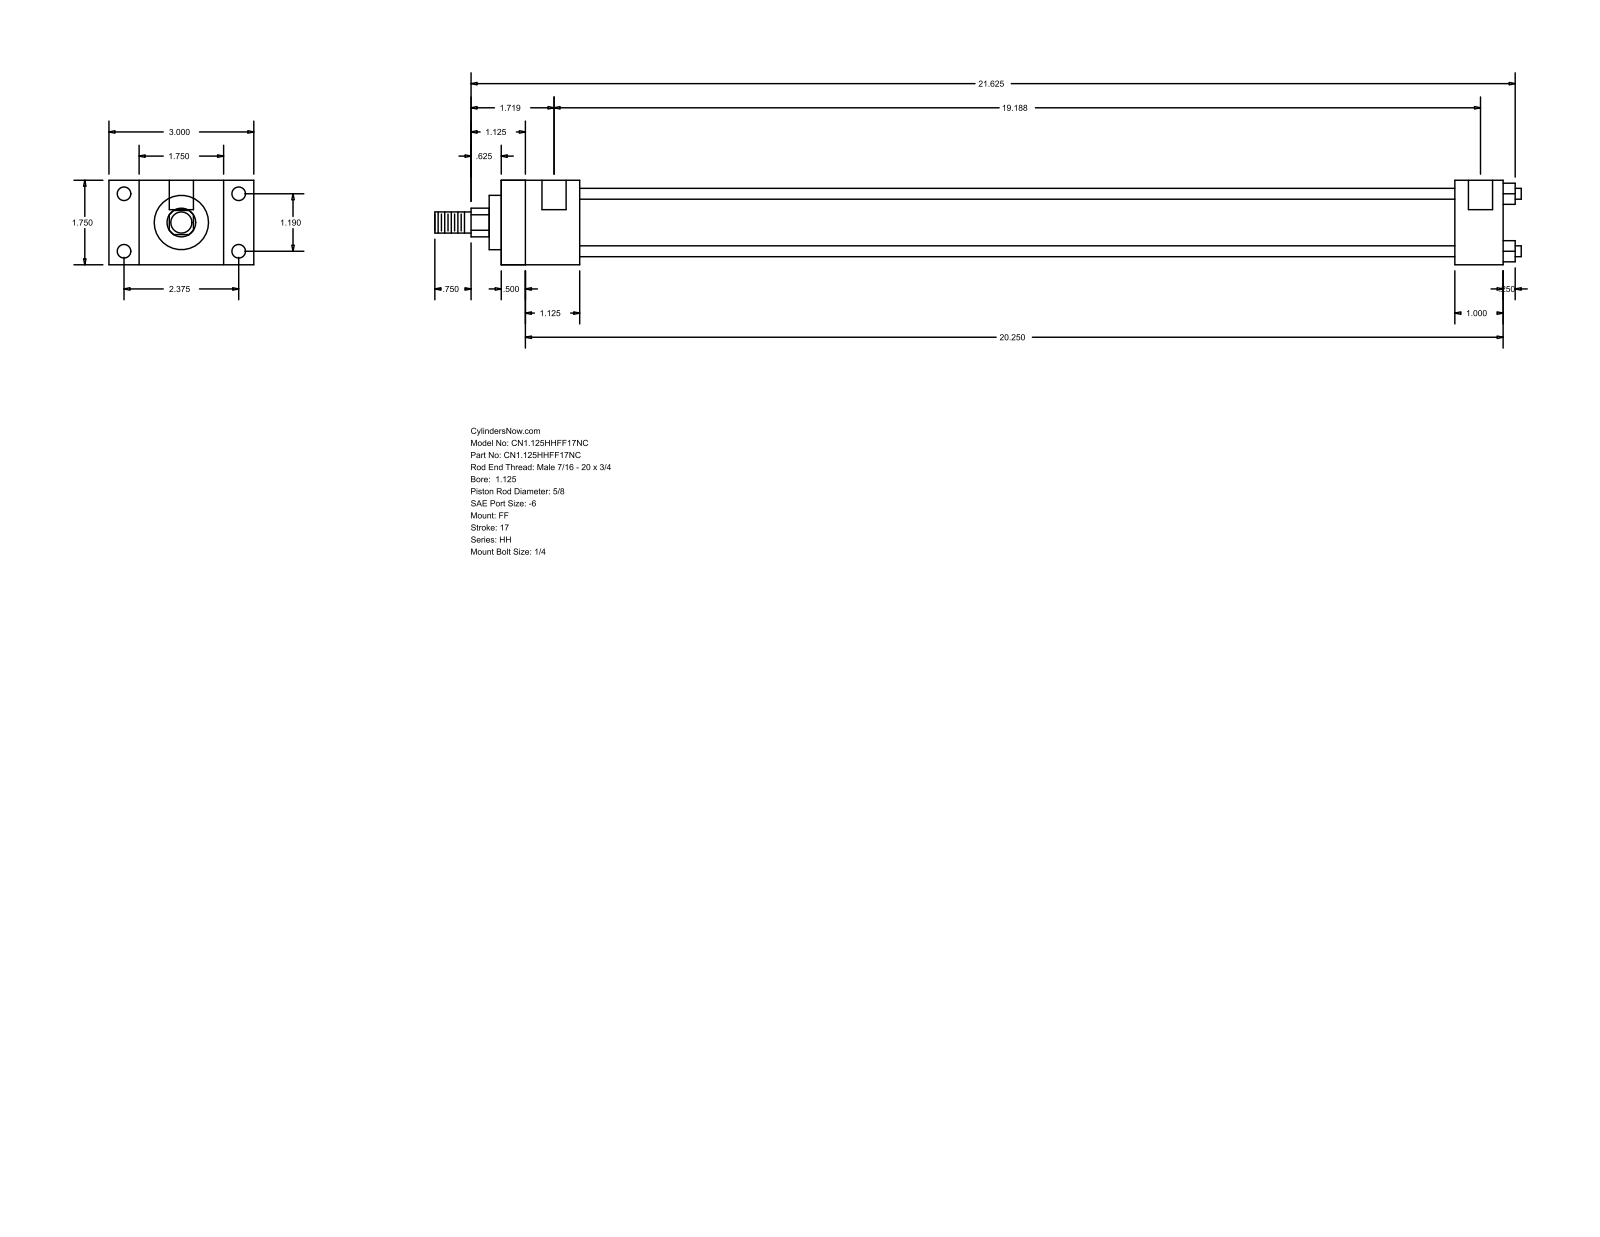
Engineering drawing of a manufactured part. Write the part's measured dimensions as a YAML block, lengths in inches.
part_name: "HH_FF__0112_0.625"
step_written_by: "GSSL Pune (CONFIG_CONTROL_DESIGN)"
units: inches
bodies: {solids: 0, faces: 92, planar: 64, cylindrical: 28, other: 0}
overall_size: [22.5, 3, 1.75]
round_holes:
  - {diameter: 0.219, count: 4}
  - {diameter: 0.281, count: 4}
  - {diameter: 0.5, count: 2}
round_bosses_or_shafts:
  - {diameter: 0.225, count: 4}
  - {diameter: 1.375, count: 1}
  - {diameter: 1.125, count: 1}
  - {diameter: 0.625, count: 1}
  - {diameter: 0.437, count: 1}
partial_cylinders:
  - {radius: 0.297, count: 1}
face_to_face_distances: [1.75, 20.75, 0.625, 0.5, 20.25, 1.125, 2.375, 1, 1.625, 19.75]
hole_center_spacings: [1.19, 2.375, 2.656, 19.063, 0.125, 19.187]
